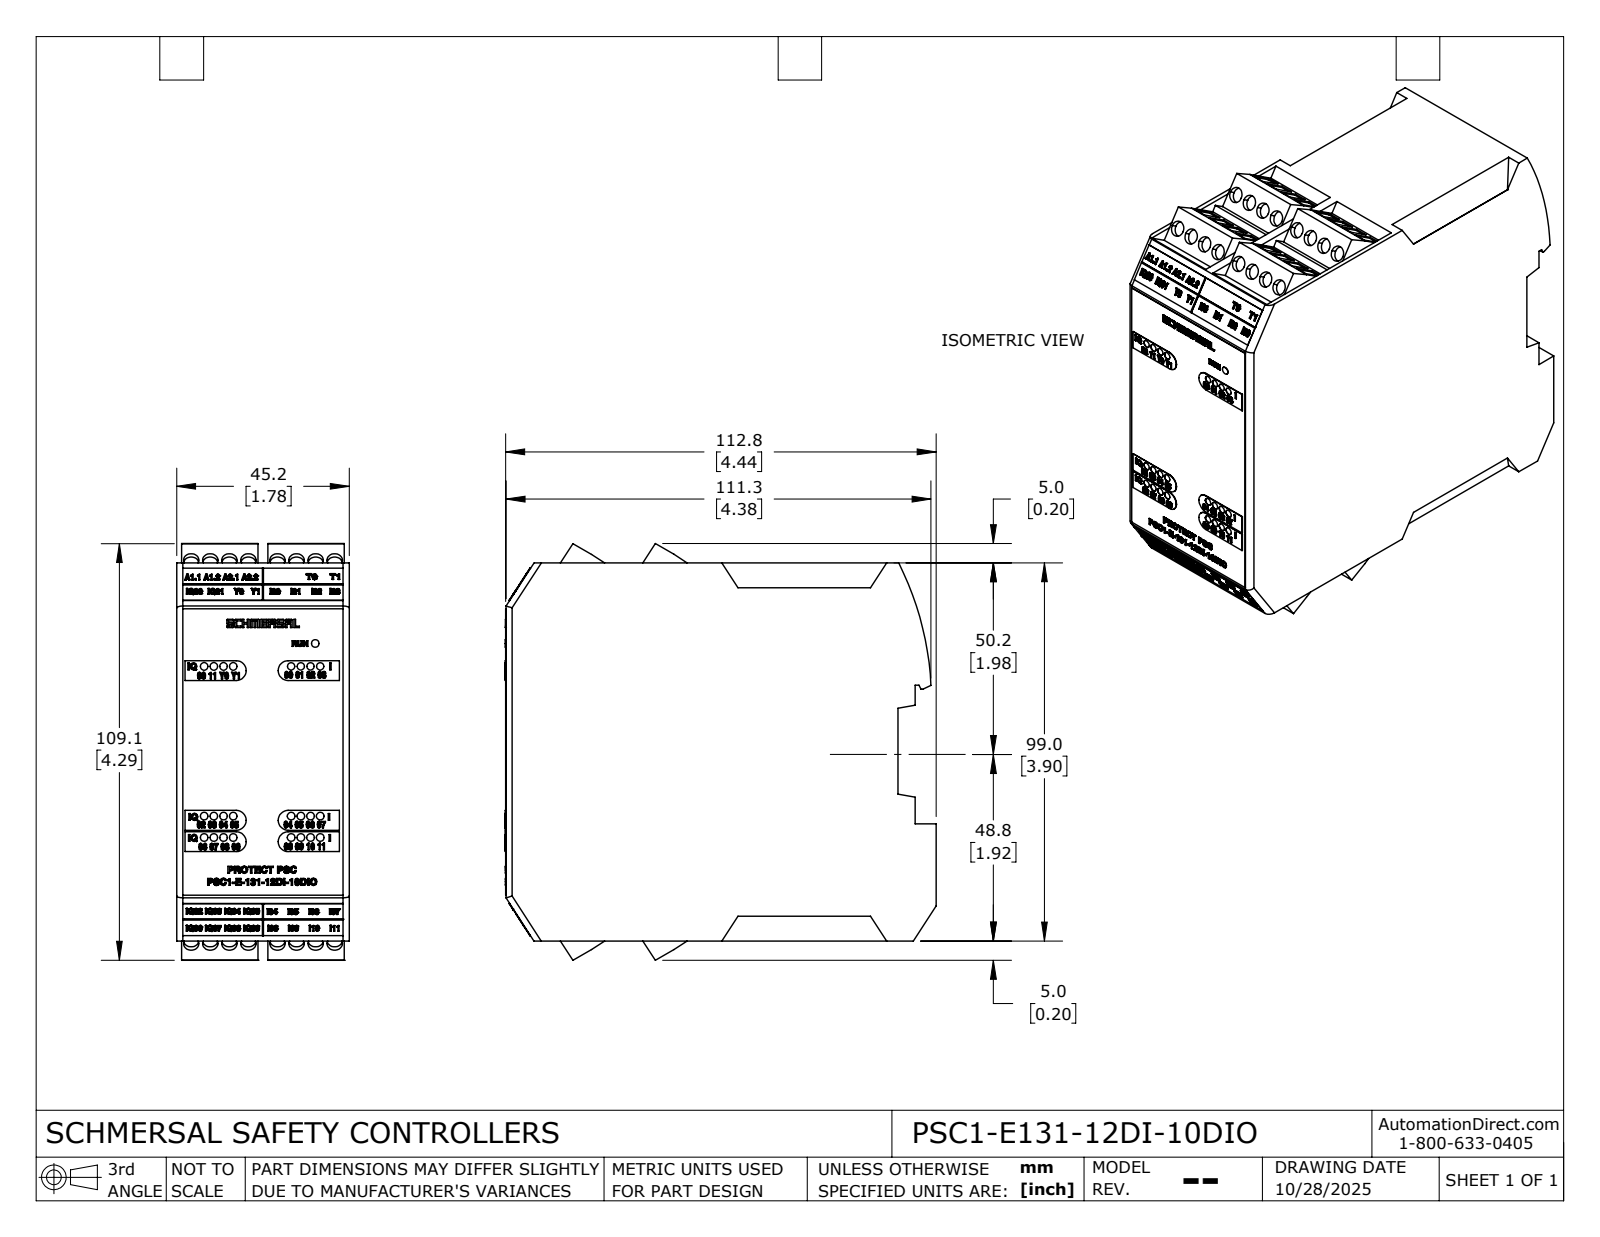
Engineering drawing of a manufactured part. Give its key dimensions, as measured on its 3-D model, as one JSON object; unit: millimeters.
{"part_name": "PSC1-E131-12DI-10DIO", "step_written_by": "SolidWorks 2024 (AUTOMOTIVE_DESIGN)", "units": "millimeters", "bodies": {"solids": 1, "faces": 3600, "planar": 1462, "cylindrical": 133, "other": 2005}, "overall_size": [112.9, 109.09, 45.2], "volume_mm3": 478327, "surface_area_mm2": 46508, "round_holes": [[4, 32], [2, 20], [1.89, 4]], "round_bosses_or_shafts": [[2, 1]], "partial_cylinders_radius": [[1.6, 6], [2.6, 6], [80, 1]], "face_to_face_distances": [45.2, 22.6, 20.05, 99, 20, 1.3, 21.3, 23.9, 43.9, 20.1], "hole_center_spacings": [5, 12.78, 2.54, 10, 11.77, 15.44, 22.6, 25.48]}
